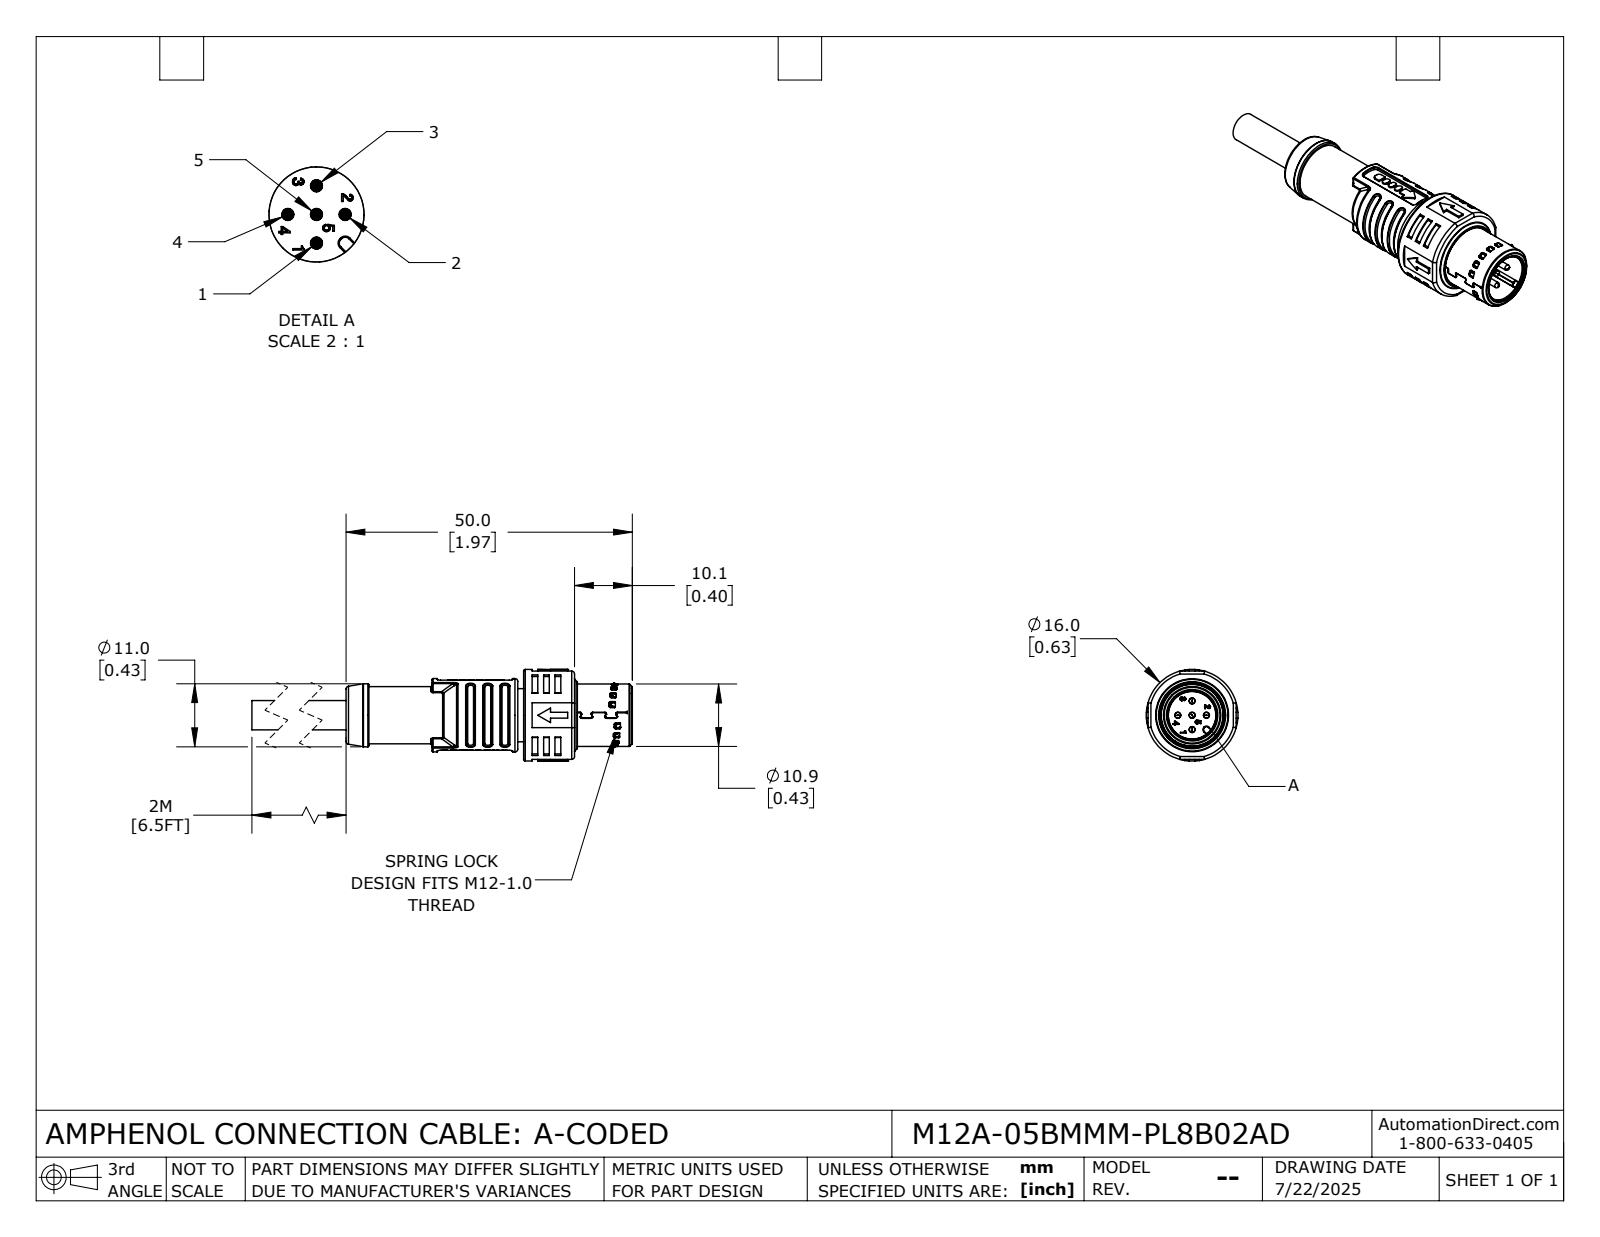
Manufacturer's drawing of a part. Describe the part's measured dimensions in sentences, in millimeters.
The part is named "M12A-05BMMM-PL8B02AD". Its 3-D file was written by "SolidWorks 2024 (CONFIG_CONTROL_DESIGN)". It is 1 solid with 2230 faces: 1085 planar, 648 cylindrical and 497 other. Overall it measures 65 by 16 by 16 millimeters. Its volume is 5 076 cubic millimeters and its surface area 5 586 square millimeters. Round holes: 5 of diameter 1.05, 1 of diameter 8.3, 1 of diameter 9, 1 of diameter 10.15, 1 of diameter 10.5, 1 of diameter 10.9, 1 of diameter 11.5, 1 of diameter 11.8, 1 of diameter 14.2. Round bosses or shafts: 5 of diameter 1, 1 of diameter 16, 1 of diameter 14.1, 1 of diameter 12.8, 1 of diameter 12.4, 1 of diameter 11, 1 of diameter 10.45, 1 of diameter 10.4. Partial cylindrical surfaces (rounded edges, fillets, slot ends): 114 of radius 0.2, 66 of radius 0.25, 64 of radius 0.3, 44 of radius 0.15, 38 of radius 0.5, 12 of radius 0.13, 11 of radius 0.7, 10 of radius 0.1. The main face-to-face distances are 1, 10.1, 8.9, 8.6, 2.5, 30, 1.5, 1.2, 32.5, 15.4. The hole center spacings are 2.5, 3.54, 5.
